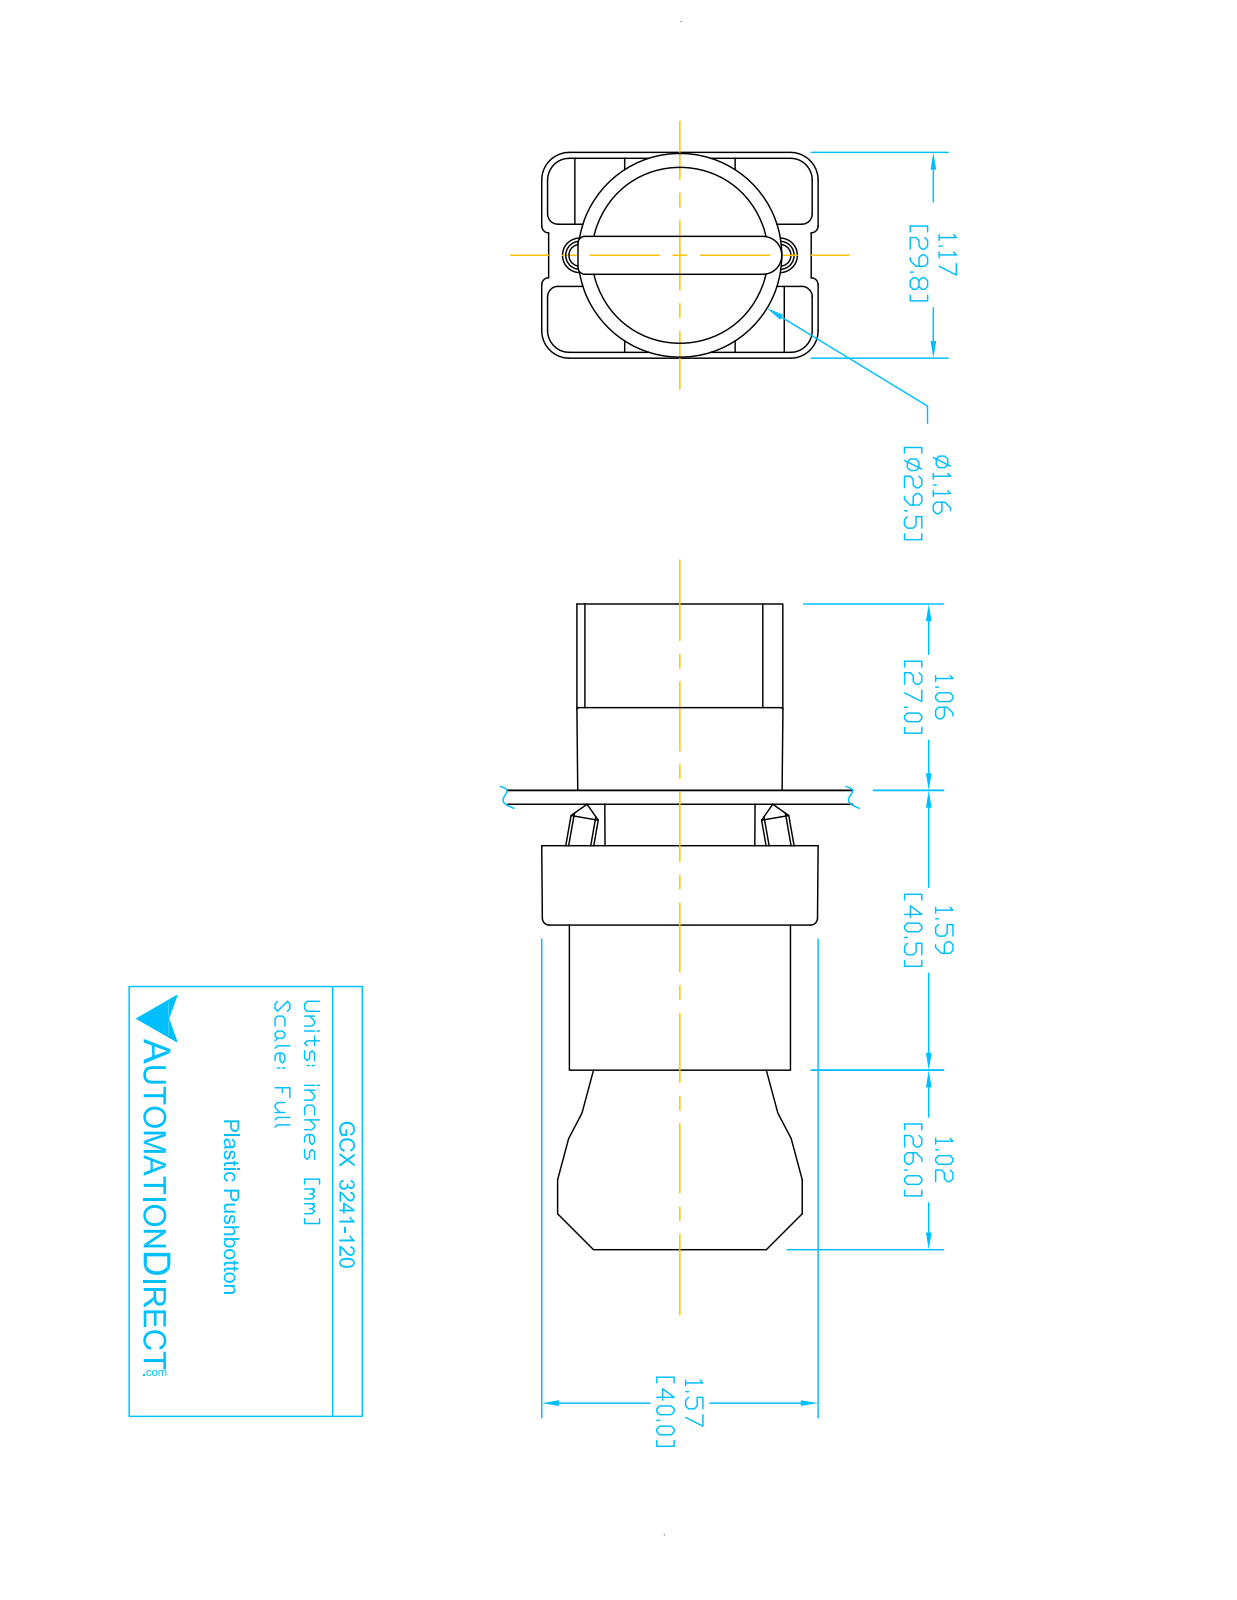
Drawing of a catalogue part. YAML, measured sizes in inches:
part_name: "ECX1050; ecx1040; GCX3241-120; GCX3241 OPERATOR (+1 more)"
step_written_by: "SolidWorks 2016 (AUTOMOTIVE_DESIGN)"
units: inches
bodies: {solids: 8, faces: 445, planar: 263, cylindrical: 151, other: 31}
overall_size: [3.653, 1.581, 1.177]
volume: 2.799
surface_area: 39
round_holes:
  - {diameter: 0.079, count: 2}
  - {diameter: 0.124, count: 2}
  - {diameter: 0.13, count: 2}
  - {diameter: 0.087, count: 1}
  - {diameter: 0.197, count: 1}
  - {diameter: 0.469, count: 1}
  - {diameter: 0.878, count: 1}
  - {diameter: 0.888, count: 1}
  - {diameter: 1.024, count: 1}
round_bosses_or_shafts:
  - {diameter: 0.157, count: 4}
  - {diameter: 1.175, count: 1}
  - {diameter: 1.004, count: 1}
  - {diameter: 0.945, count: 1}
  - {diameter: 0.856, count: 1}
  - {diameter: 0.78, count: 1}
  - {diameter: 0.504, count: 1}
partial_cylinders:
  - {radius: 0.059, count: 24}
  - {radius: 0.041, count: 12}
  - {radius: 0.124, count: 12}
  - {radius: 0.157, count: 12}
  - {radius: 0.039, count: 9}
  - {radius: 0.128, count: 2}
  - {radius: 0.02, count: 1}
  - {radius: 0.063, count: 1}
face_to_face_distances: [0.827, 2.02, 1.193, 0.579, 1.244, 1.171, 0.472, 0.469, 0.031, 0.033]
hole_center_spacings: [0.236, 0.544, 0.472, 0.49]
